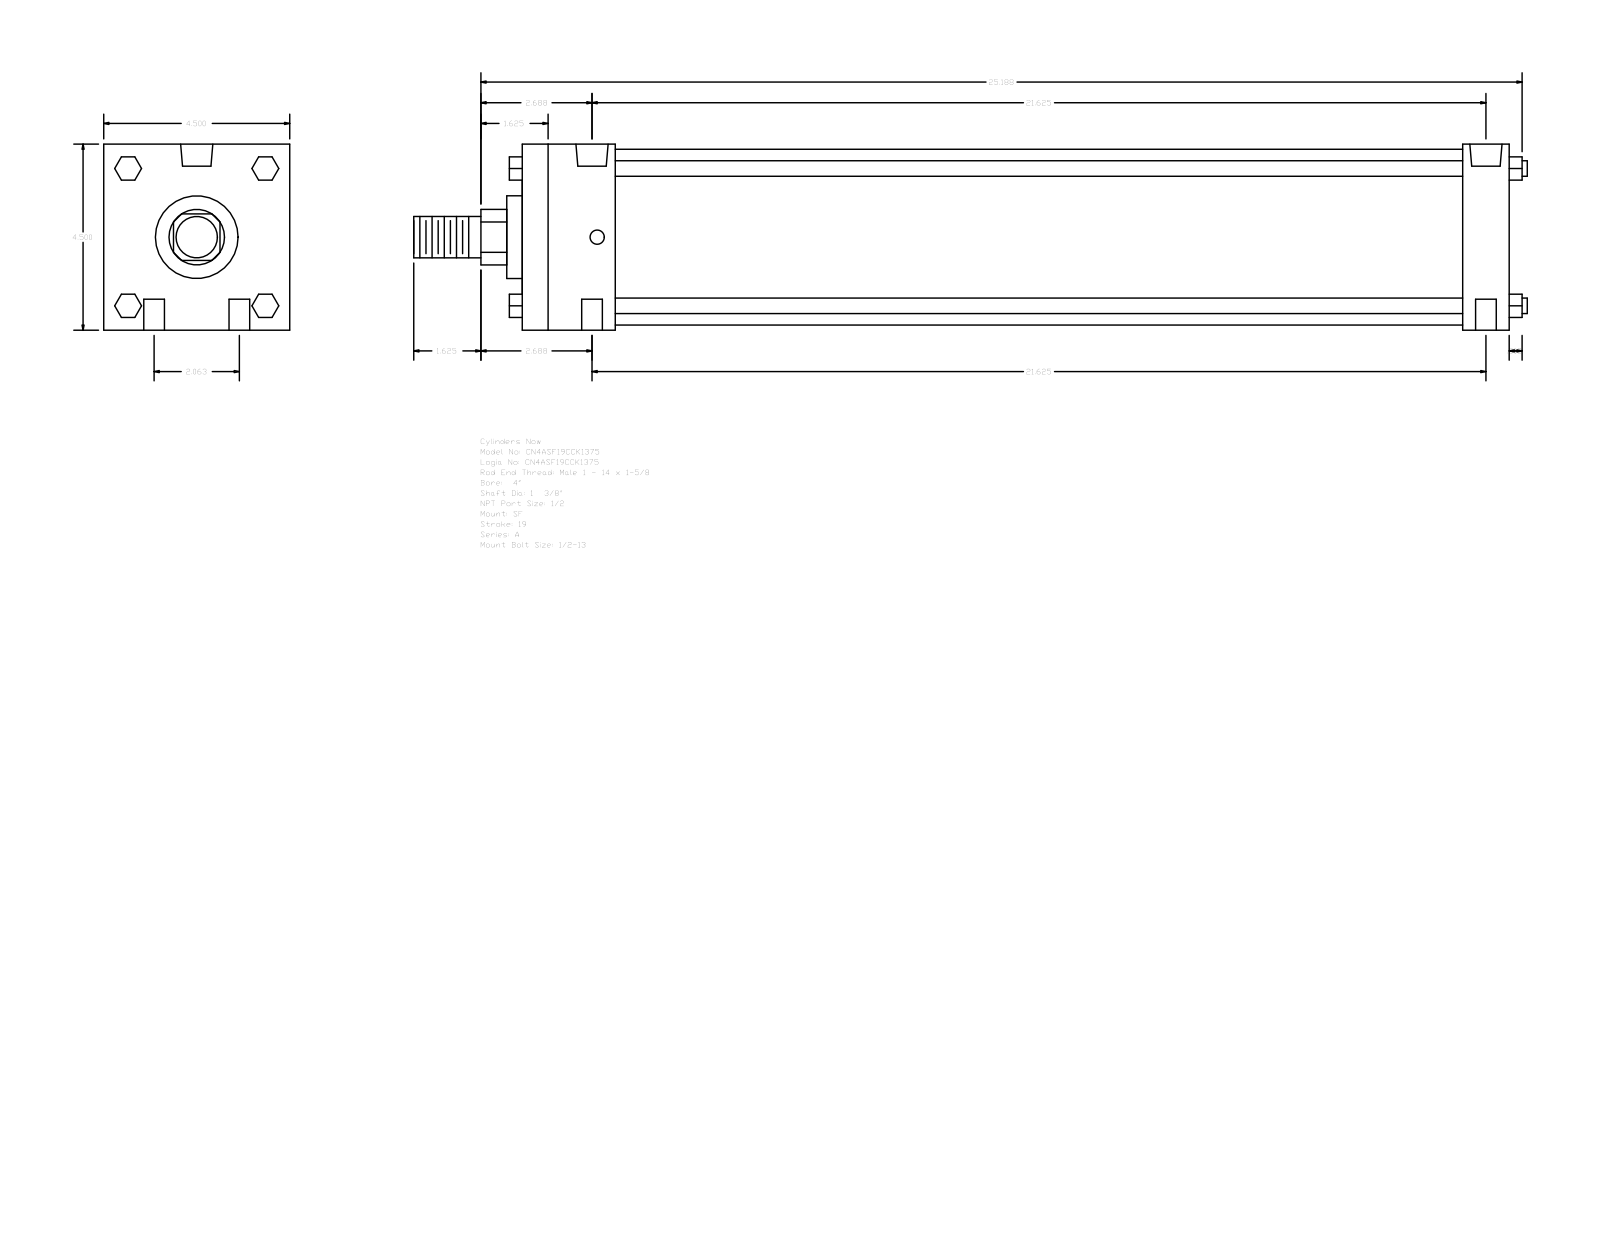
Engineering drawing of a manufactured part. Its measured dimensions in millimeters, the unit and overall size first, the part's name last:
Units: millimetres
Overall size (bounding box): 684.21 × 114.3 × 114.3
Round holes (diameter × count): ⌀12.7 ×4, ⌀8.73 ×2, ⌀19.77 ×2
Round bosses / shafts (diameter × count): ⌀9.53 ×4, ⌀107.95 ×1, ⌀50.8 ×1, ⌀34.92 ×1, ⌀25.4 ×1
Partial cylindrical surfaces — rounded edges, fillets, slot ends (radius × count): R17.06 ×1
Main face-to-face distances: 114.3, 606.43, 57.15, 28.58, 577.85, 520.7, 549.28, 66.67, 14.29, 9.52
Hole centre spacings: 26.19, 549.9, 549.28, 52.38, 551.77, 542.92
Bodies: 0 solids, 124 faces (94 planar, 30 cylindrical, 0 other)
Part name (STEP PRODUCT): A_SF__0400_1.375
STEP written by: GSSL Pune (CONFIG_CONTROL_DESIGN)
